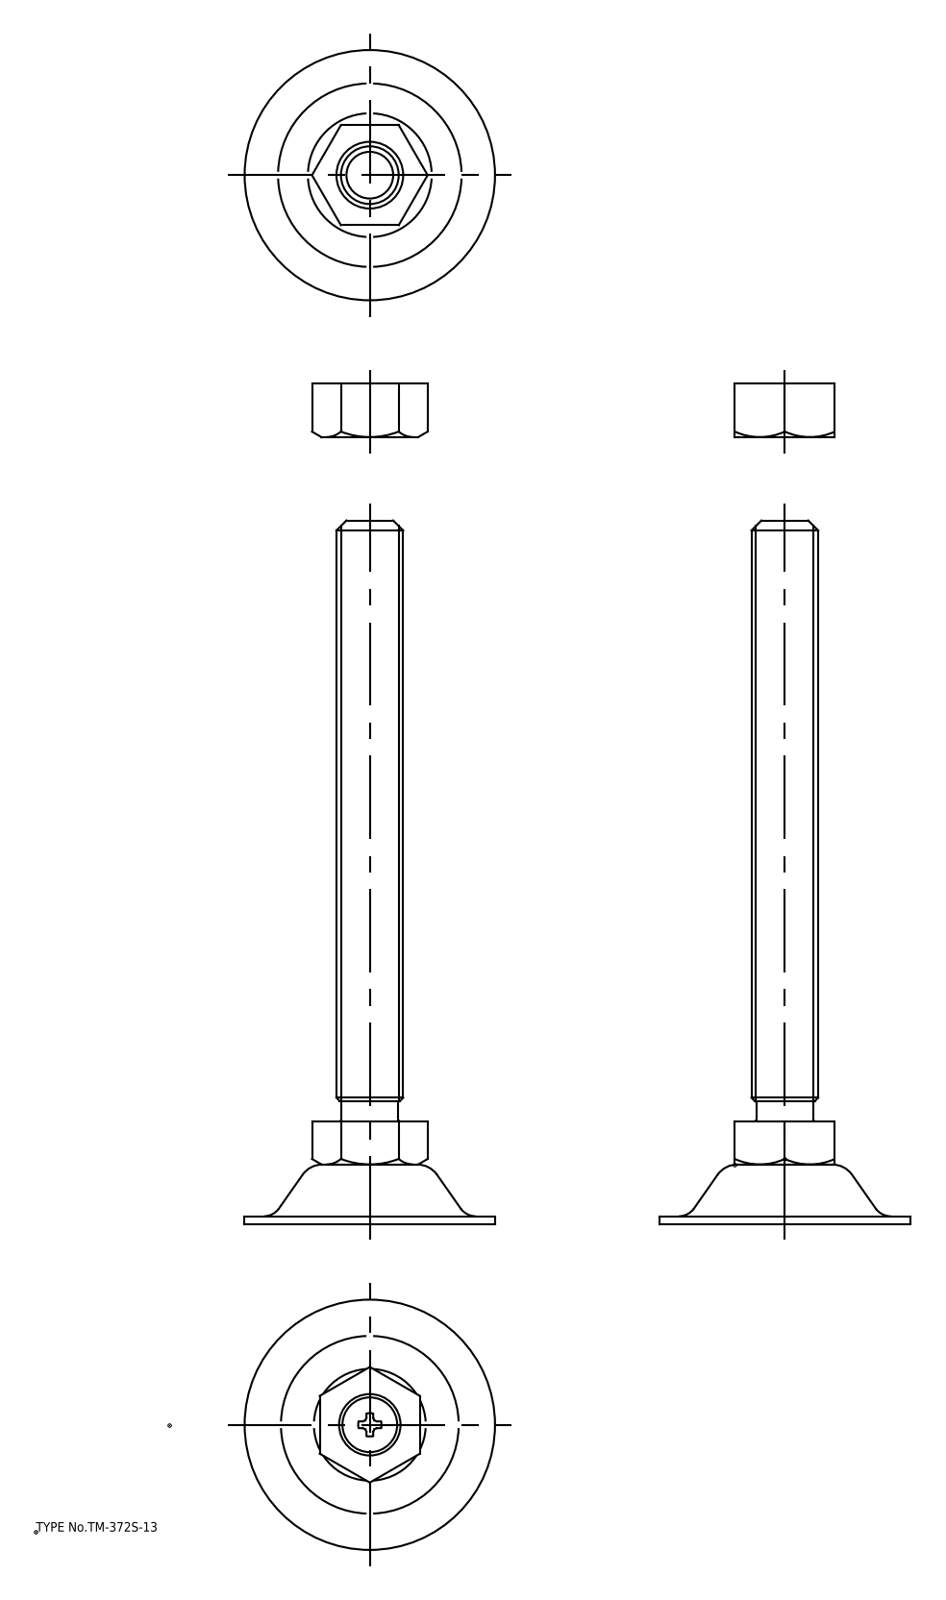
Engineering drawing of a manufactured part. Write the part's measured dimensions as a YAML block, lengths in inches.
part_name: "アジャストボルト; ナット; フット"
step_written_by: "spGate 18.9.1 (****-****-****-****) (AUTOMOTIVE_DESIGN)"
units: inches
bodies: {solids: 3, faces: 90, planar: 48, cylindrical: 18, other: 24}
overall_size: [8.309, 2.953, 2.953]
volume: 5.834
surface_area: 48.11
round_holes:
  - {diameter: 0.724, count: 1}
  - {diameter: 0.748, count: 1}
round_bosses_or_shafts:
  - {diameter: 2.953, count: 1}
  - {diameter: 0.787, count: 1}
partial_cylinders:
  - {radius: 0.138, count: 1}
face_to_face_distances: [1.181, 0.098, 0.61, 0.512, 0.612, 0.159, 0.061, 4.194, 4.096, 4.035]
